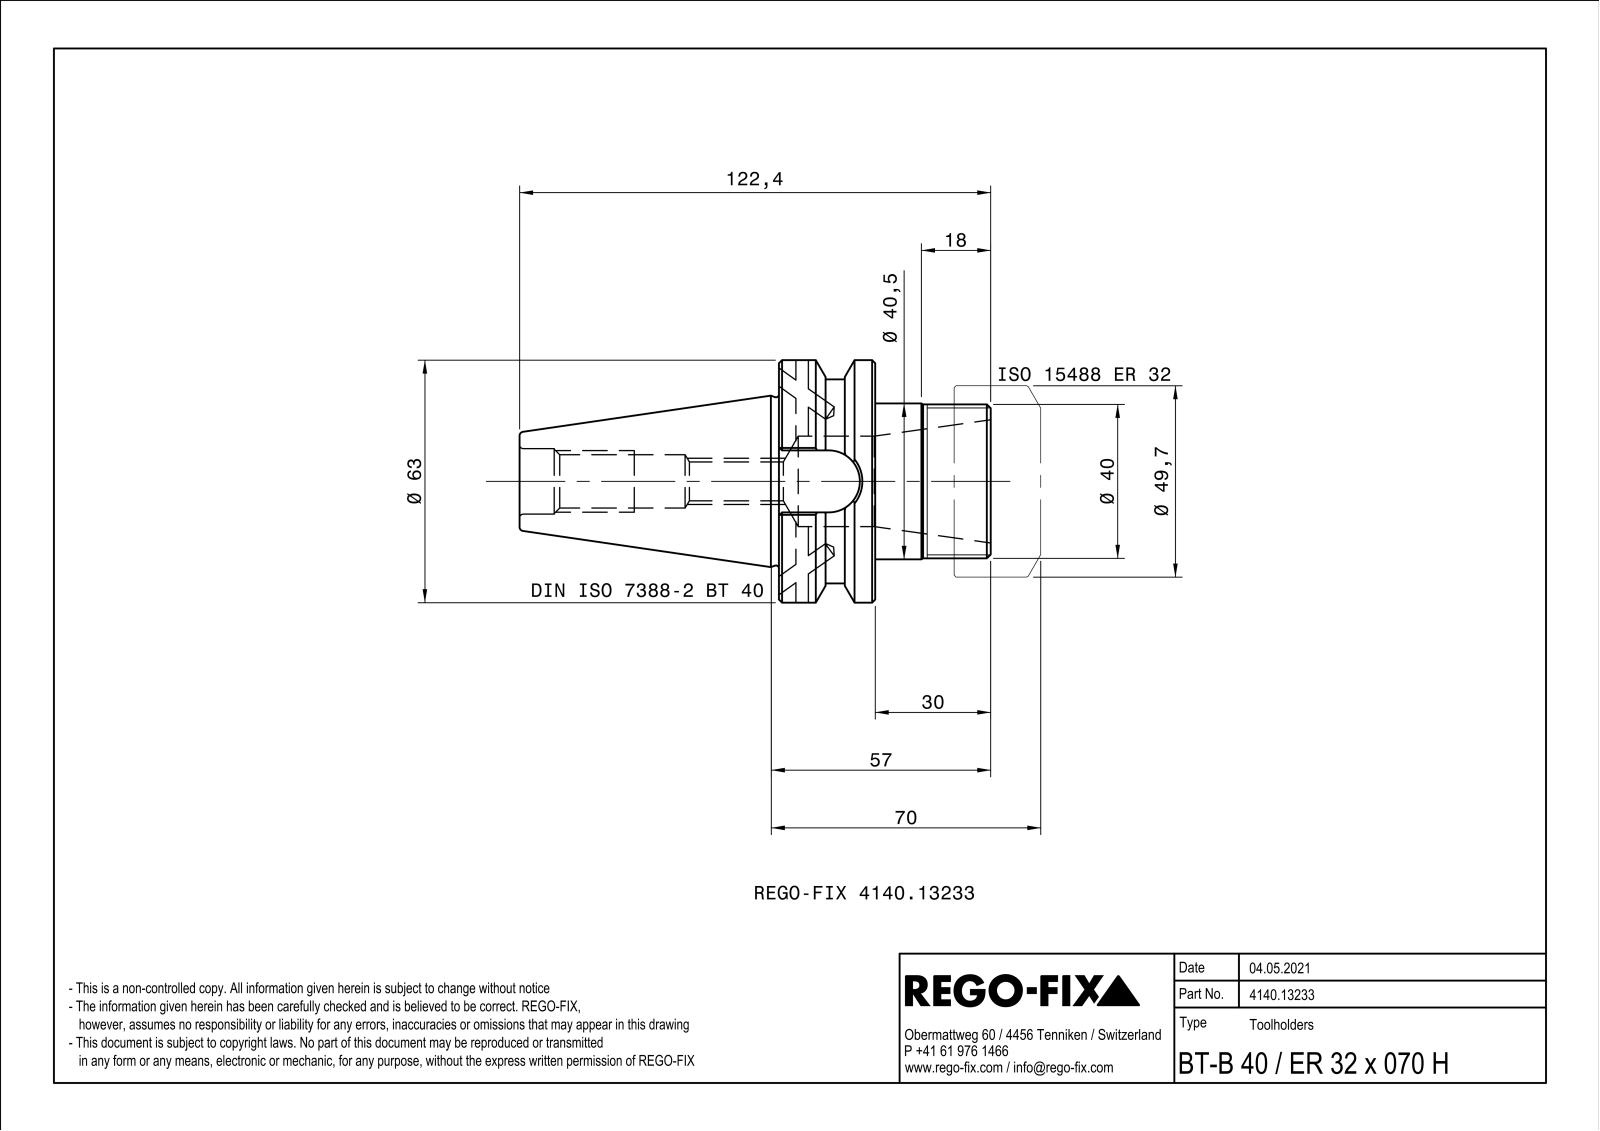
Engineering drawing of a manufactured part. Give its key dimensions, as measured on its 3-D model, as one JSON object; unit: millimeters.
{"part_name": "NOCUT", "step_written_by": "SIEMENS PLM Software Solid Edge ST10 (AUTOMOTIVE_DESIGN)", "units": "millimeters", "bodies": {"solids": 1, "faces": 107, "planar": 37, "cylindrical": 31, "other": 39}, "overall_size": [122.4, 63, 63], "volume_mm3": 134503, "surface_area_mm2": 29247, "round_holes": [[3.24, 2], [3.9, 2], [10.11, 1], [13.83, 1], [13.84, 1], [17, 1], [23.5, 1]], "round_bosses_or_shafts": [[63, 1], [53, 1], [40.5, 1], [40, 1]], "partial_cylinders_radius": [[0.5, 4], [8.05, 1]], "face_to_face_distances": [25, 30, 55, 45.1, 122.4, 92.4, 67.4, 16.1, 37.9, 7.9]}
